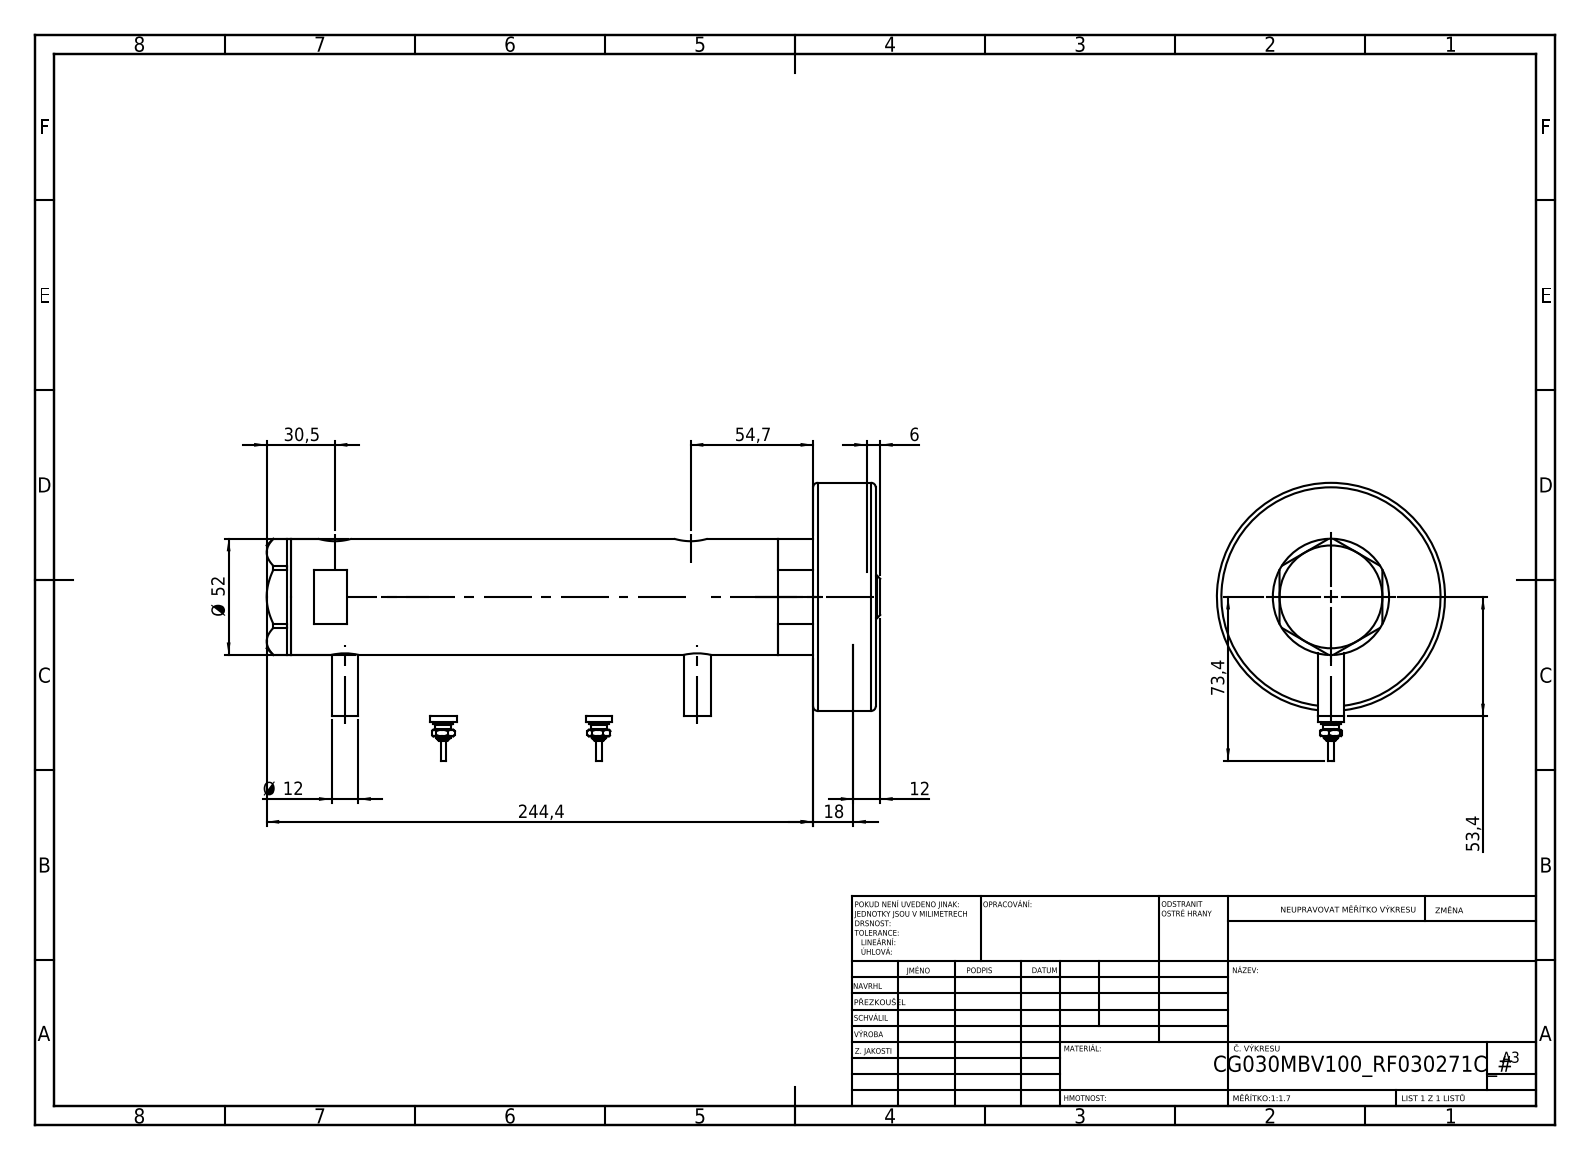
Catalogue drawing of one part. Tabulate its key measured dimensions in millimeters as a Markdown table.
| quantity | value |
| --- | --- |
| part name | V270CG_BACK; V270CG_FRONT; V270CG_MIDDLE; Switch (+2 more) |
| STEP written by | SolidWorks 2019 (CONFIG_CONTROL_DESIGN) |
| units | millimeters |
| bodies | 7 solids, 236 faces (95 planar, 73 cylindrical, 68 other) |
| overall size | 274.4 × 124.4 × 102 |
| volume | 697 645 mm³ |
| surface area | 135 148 mm² |
| round holes (diameter × count) | 9.73 × 2, 12.5 × 2, 15 × 2, 6.5 × 1, 20 × 1, 21.5 × 1, 30 × 1, 33 × 1, 40 × 1, 44 × 1 |
| round bosses / shafts (diameter × count) | 12 × 4, 9 × 2, 7 × 2, 4.5 × 2, 2.5 × 2, 102 × 1, 52 × 1, 38 × 1 |
| main face-to-face distances | 28, 233.4, 261.4, 181.5, 51.9, 79.9, 23.8, 157.7, 209.6, 237.6 |
| hole center spacings | 2.9, 4.5, 154.7, 157.6, 159.2, 162.1 |
